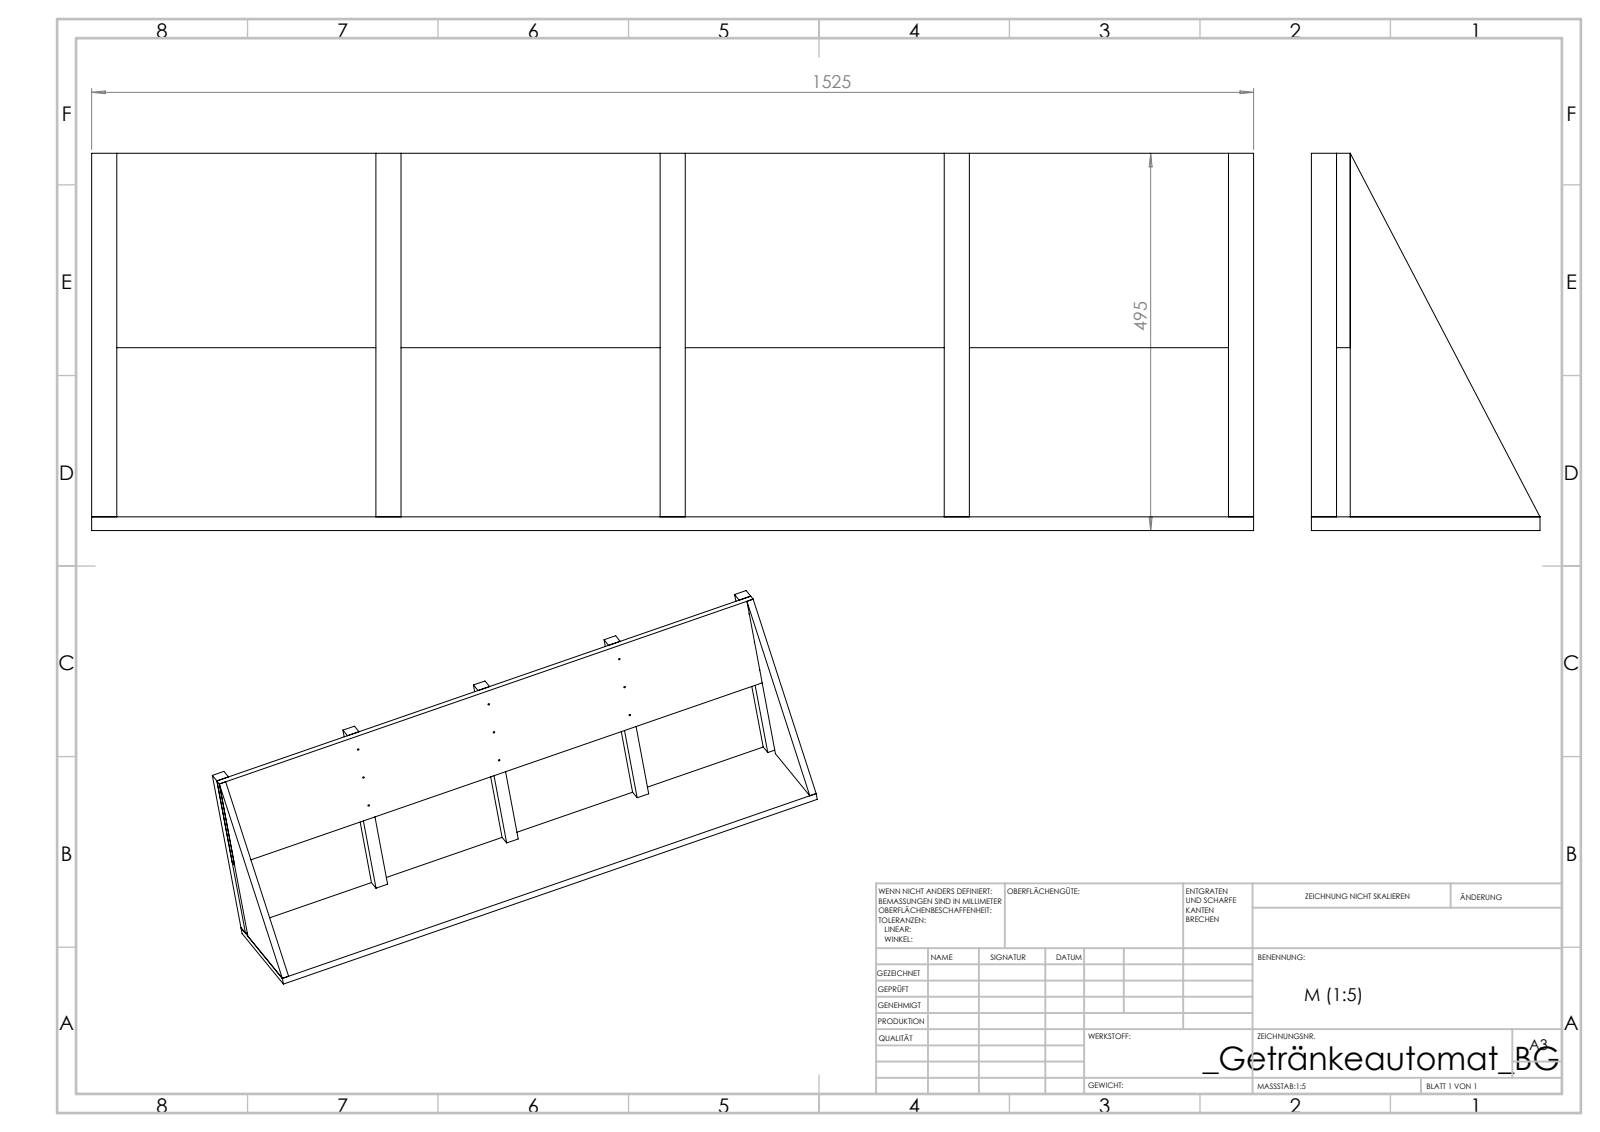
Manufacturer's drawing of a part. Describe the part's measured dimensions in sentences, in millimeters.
The part is named "Säule; Rippe; Getränkeautomat_BG; Rückwand (+1 more)". Its 3-D file was written by "SolidWorks 2016 (CONFIG_CONTROL_DESIGN)". It is 9 solids with 142 faces: 52 planar, 60 cylindrical and 30 other. Overall it measures 1525 by 495 by 300 millimeters. Its volume is 19 950 000 cubic millimeters and its surface area 2 442 000 square millimeters. Round holes: 15 of diameter 4, 15 of diameter 7. The main face-to-face distances are 18, 33, 373, 1507, 51, 746, 1525, 406, 1119, 340. The hole center spacings are 383.13, 373, 751.11, 87.5, 746, 412.01, 1122.42, 766.25.
